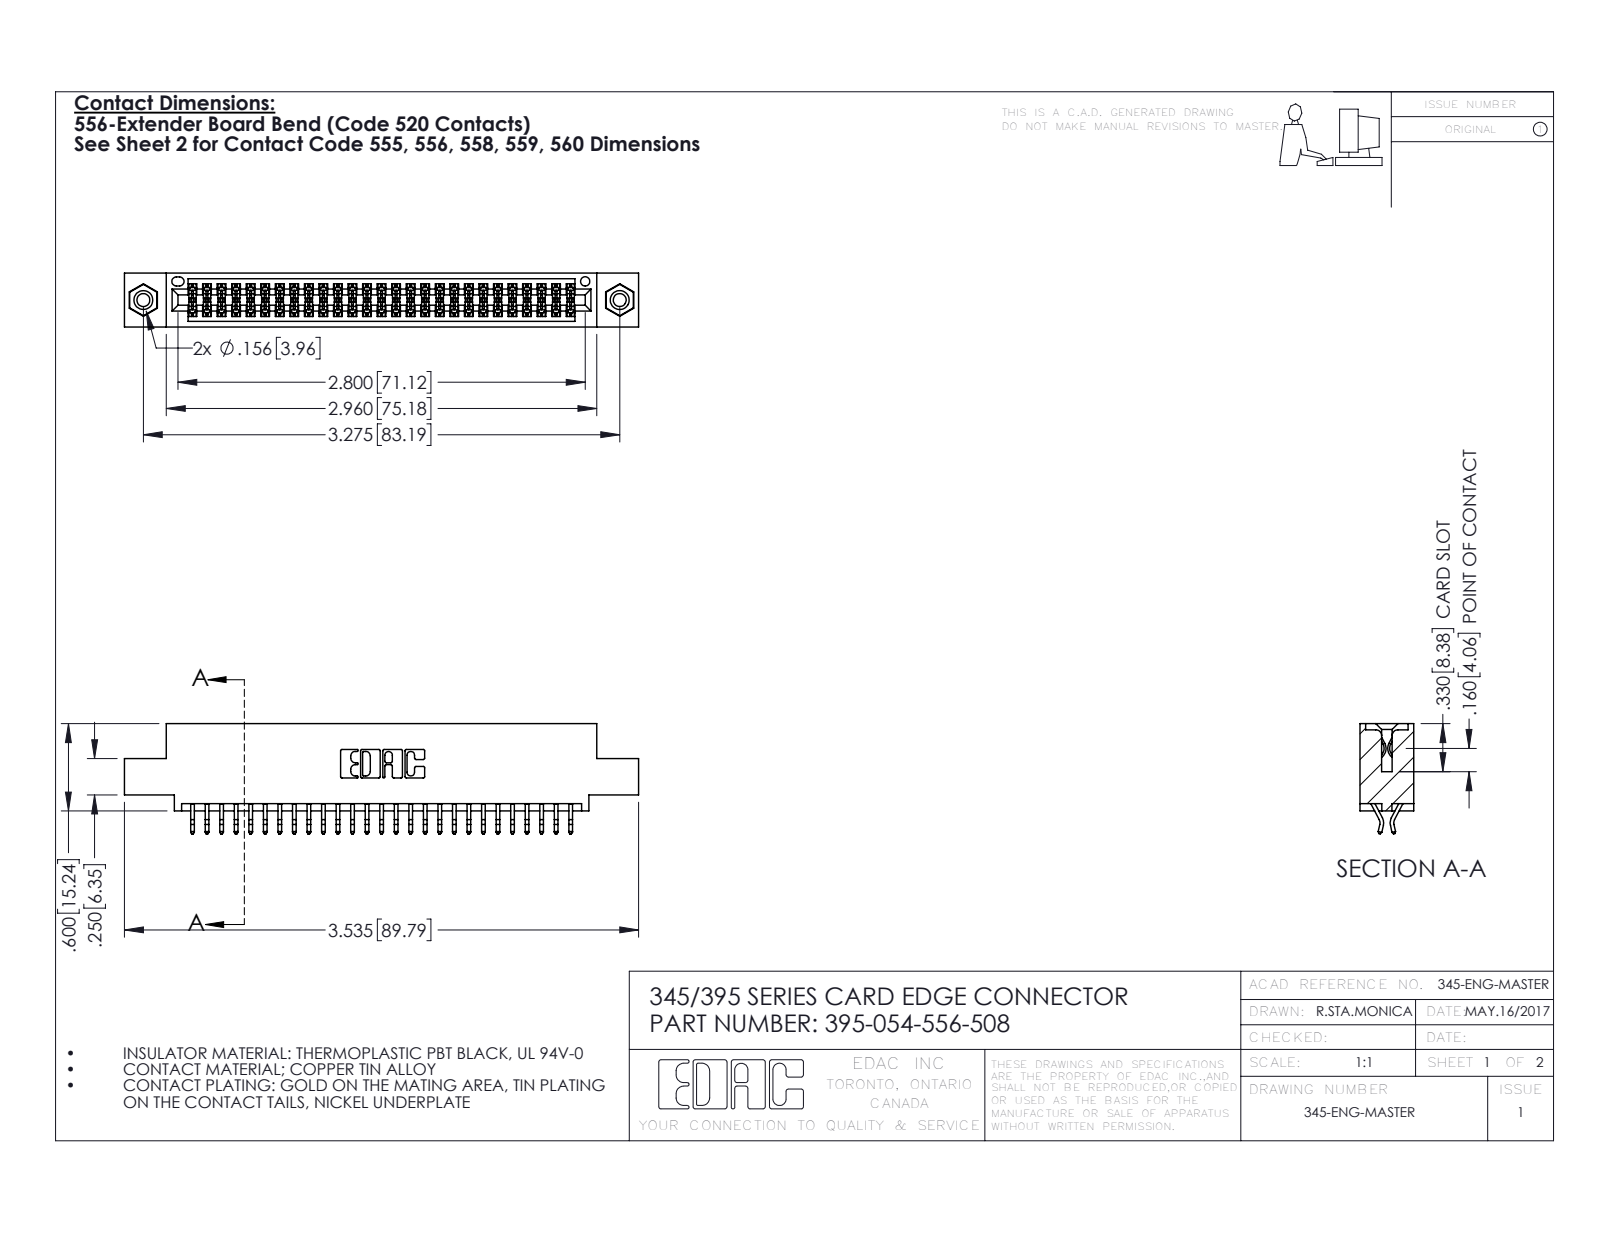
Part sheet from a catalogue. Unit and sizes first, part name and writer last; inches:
Units: inches
Overall size (bounding box): 3.535 × 0.757 × 0.37
Round holes (diameter × count): ⌀0.089 ×2, ⌀0.125 ×2, ⌀0.156 ×2, ⌀0.064 ×1
Round bosses / shafts (diameter × count): ⌀0.155 ×2
Partial cylindrical surfaces — rounded edges, fillets, slot ends (radius × count): R0.006 ×81, R0.01 ×22, R0.007 ×6, R0.031 ×6, R0.026 ×3, R0.01 ×2, R0.014 ×2, R0.019 ×2
Main face-to-face distances: 0.072, 0.298, 0.37, 0.2, 0.025, 0.098, 0.272, 0.225, 0.175, 0.149
Hole centre spacings: 0.27, 3.04, 3.275
Volume: 0.519 in³ · Surface area: 19.12 in²
Bodies: 57 solids, 3214 faces (2114 planar, 1084 cylindrical, 16 other)
Part name (STEP PRODUCT): 345-292-001_556 Tail; 345 Part_0.110 Offset - 0.156 Dia-TI; 395-054-556-508; 345-250-001_345-250-003-102
STEP written by: SolidWorks 2016 (CONFIG_CONTROL_DESIGN)
